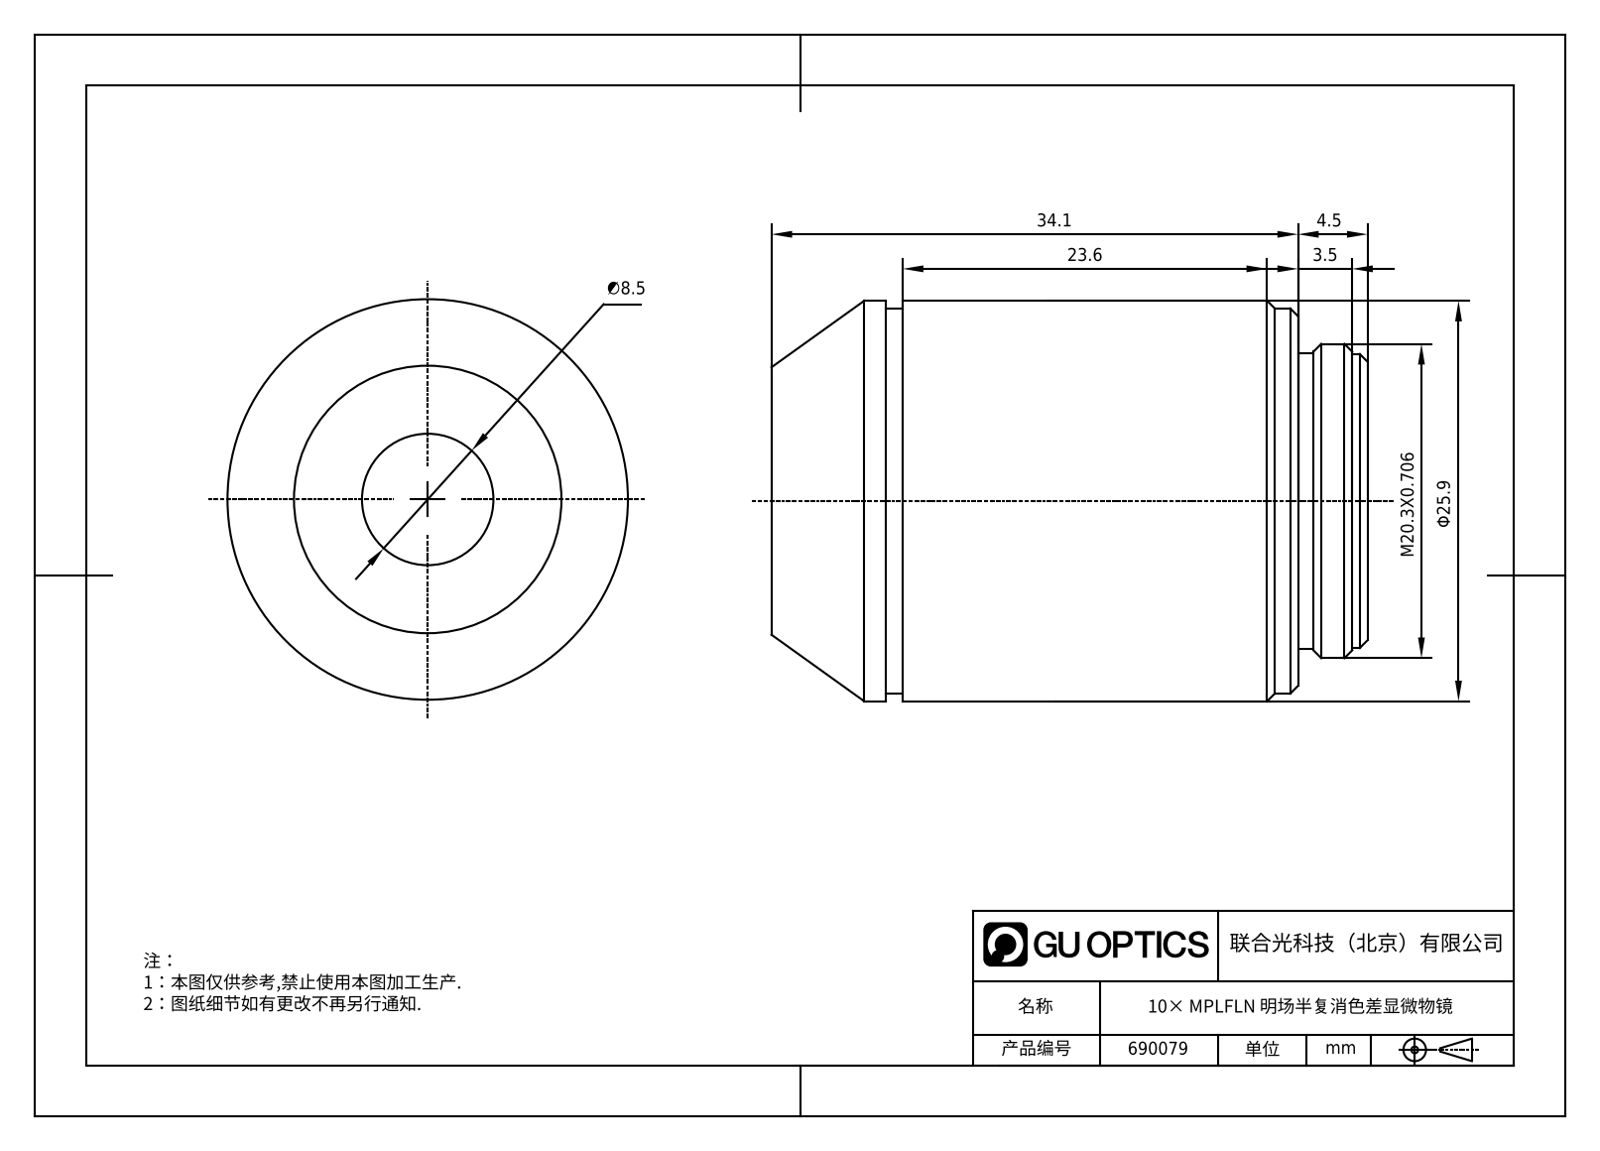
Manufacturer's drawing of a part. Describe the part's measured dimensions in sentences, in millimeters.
The part is named "690079". Its 3-D file was written by "SolidWorks 2020 (CONFIG_CONTROL_DESIGN)". It is 1 solid with 39 faces: 9 planar, 18 cylindrical and 12 other. Overall it measures 38.56 by 25.9 by 25.9 millimeters. Its volume is 18 174 cubic millimeters and its surface area 3 897 square millimeters. Round holes: 1 of diameter 8.5, 1 of diameter 10.9. Round bosses or shafts: 1 of diameter 25.9, 1 of diameter 24.9, 1 of diameter 20.32, 1 of diameter 19.1, 1 of diameter 19. The main face-to-face distances are 34.06, 4.5, 38.56, 0.61, 3.89, 37.95, 38.31, 37.7, 33.81, 30.07.
